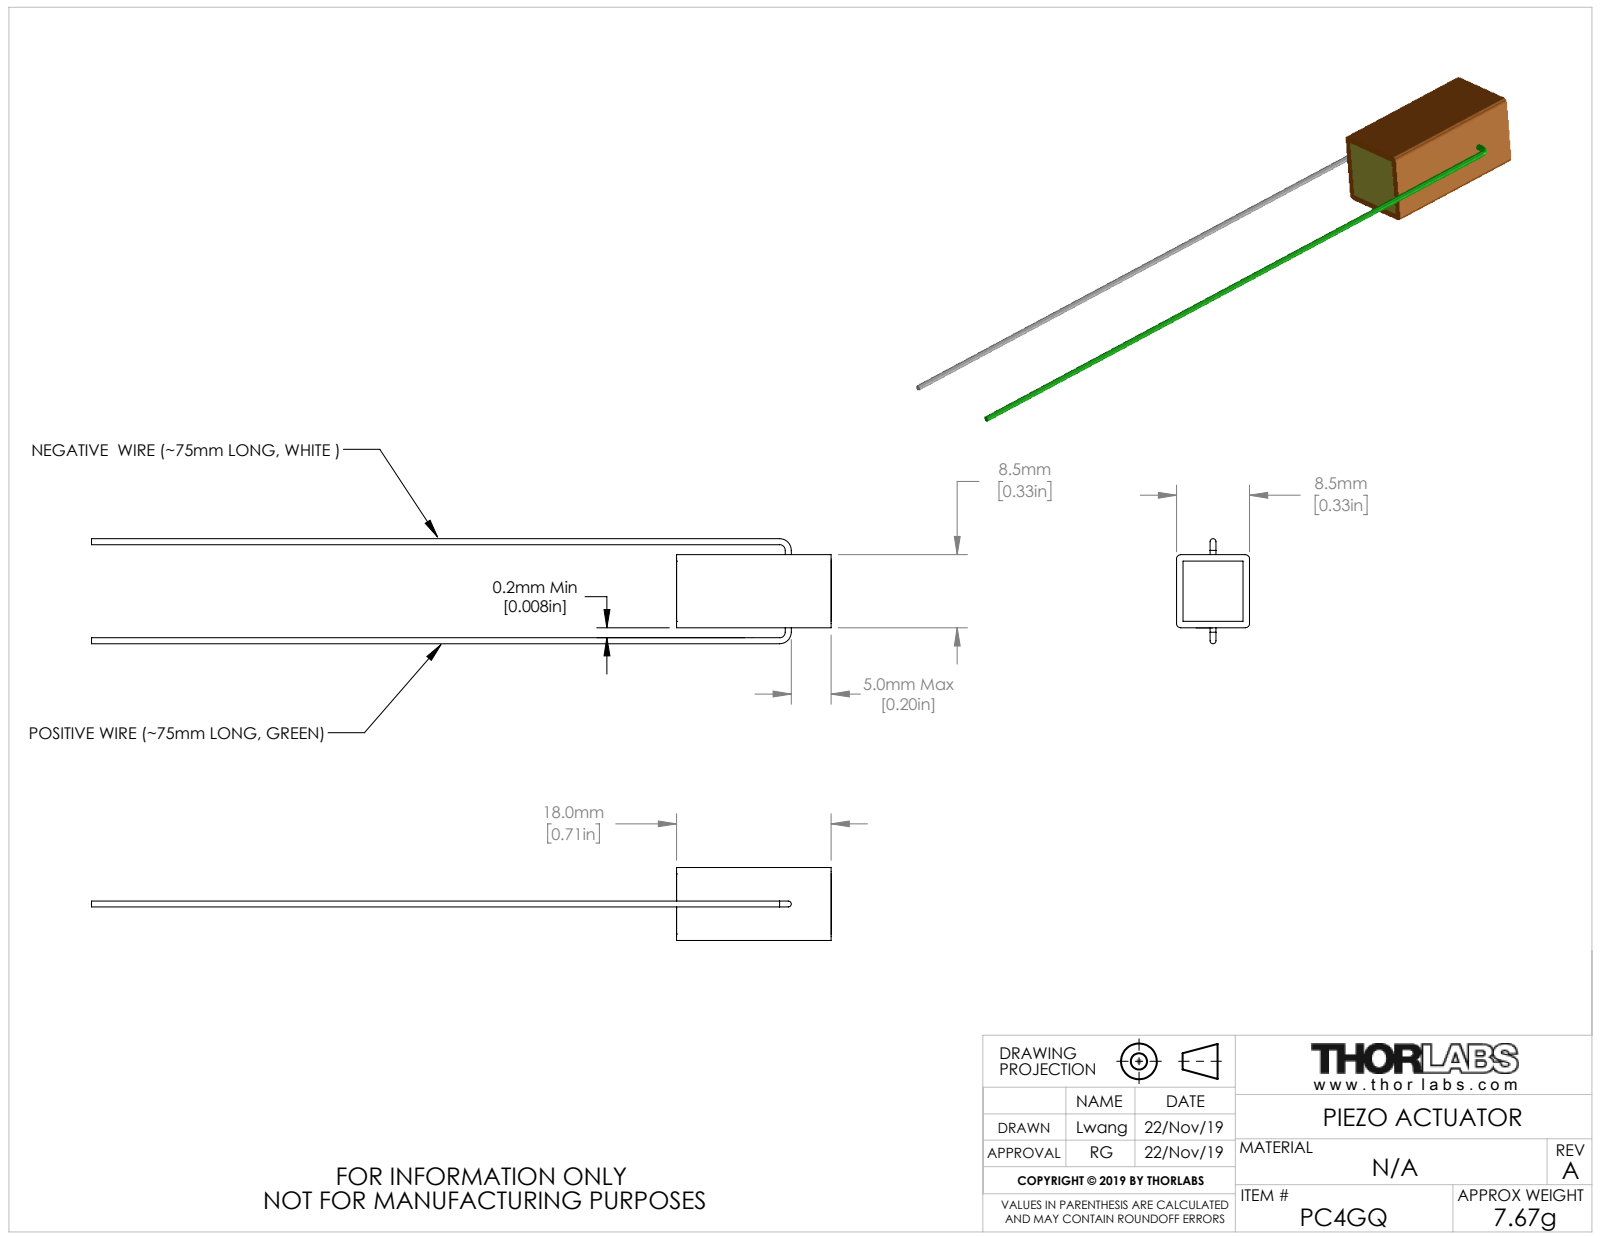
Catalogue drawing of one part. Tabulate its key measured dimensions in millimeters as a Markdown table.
| quantity | value |
| --- | --- |
| part name | CTN014848-E0W |
| STEP written by | SolidWorks 2018 (AUTOMOTIVE_DESIGN) |
| units | millimeters |
| bodies | 1 solid, 34 faces (18 planar, 12 cylindrical, 4 other) |
| overall size | 86.13 × 12.22 × 8.5 |
| volume | 1 361 mm³ |
| surface area | 1 103 mm² |
| round bosses / shafts (diameter × count) | 0.7 × 3 |
| partial cylindrical surfaces (radius × count) | 0.5 × 4 |
| main face-to-face distances | 8.5, 18.02, 18.01, 18, 68.11, 68.12, 86.12, 86.13, 0.75, 7.75 |
